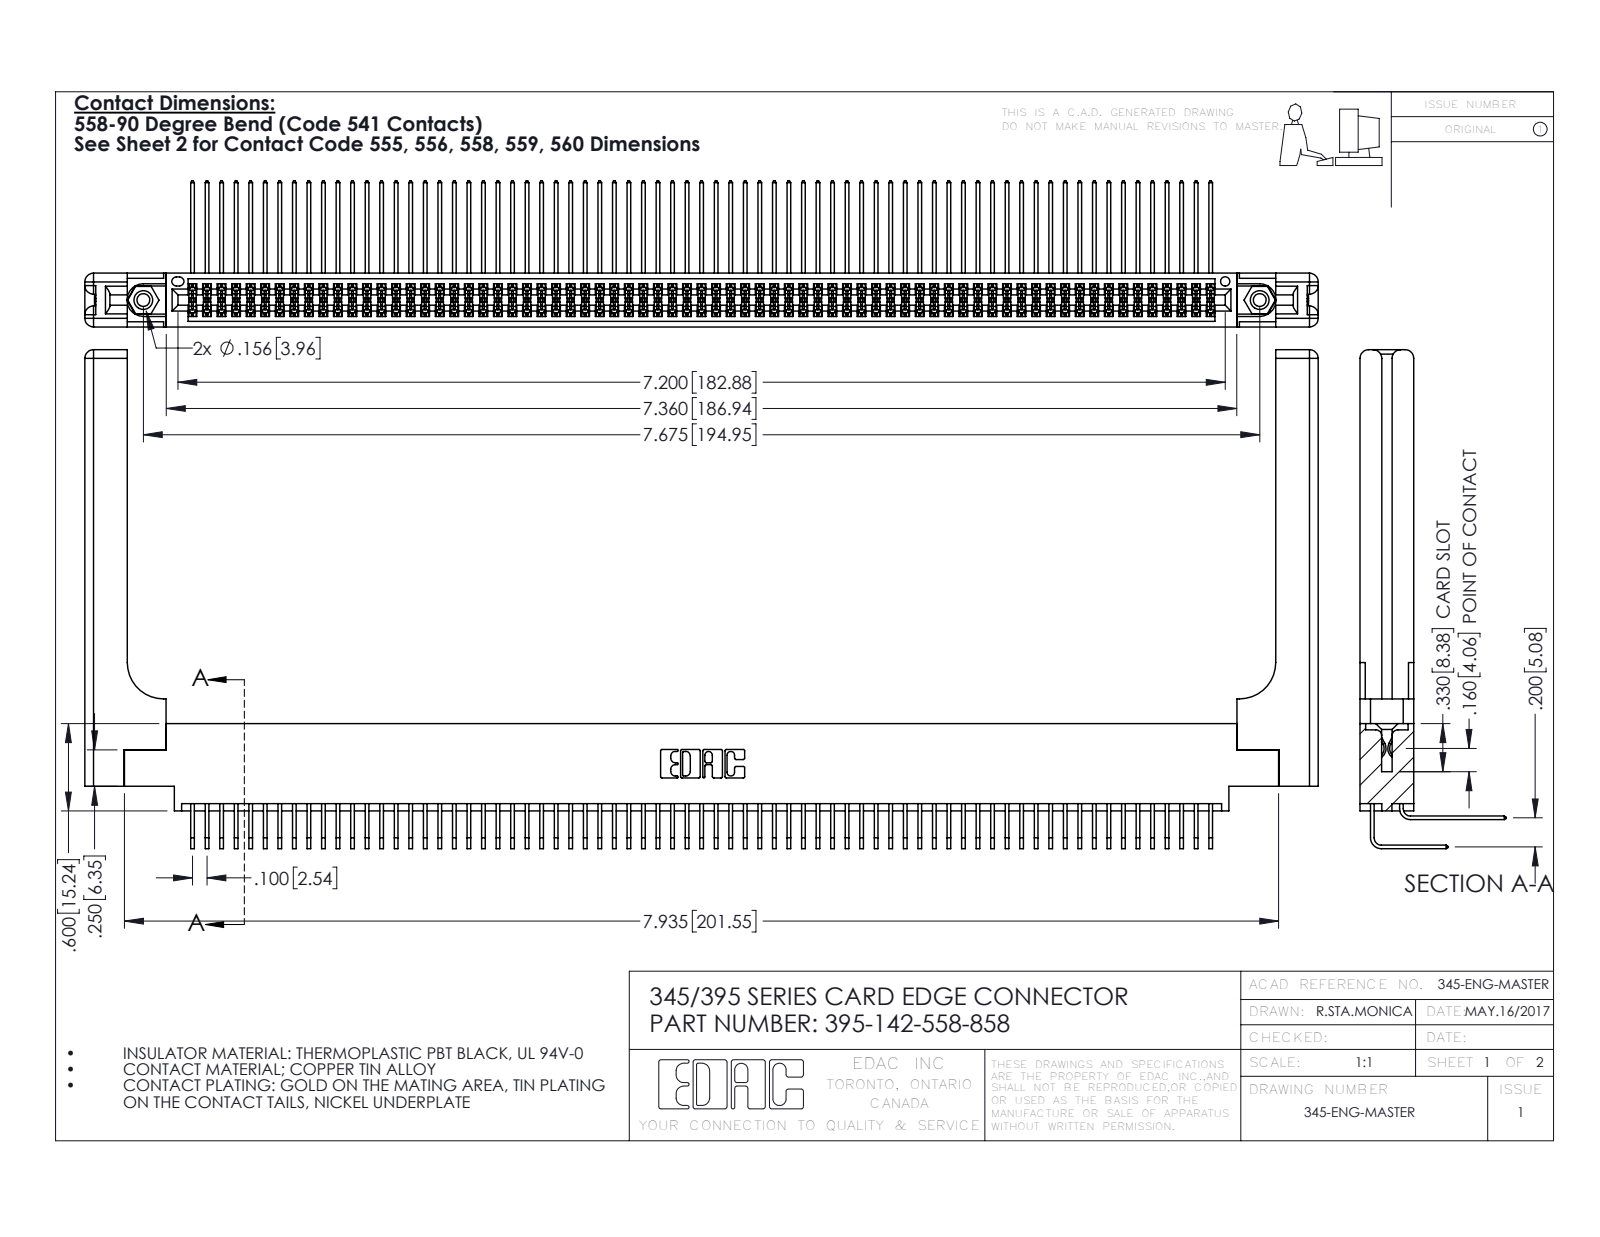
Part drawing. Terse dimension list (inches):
name: 345-250-001_345-250-001-102; 345 Part_0.170 Offset - 0.156 Dia-TH; 345-292-001_558 559 Tail - 1; 345-292-001_558 Tail - 2 (+2 more)
written by: SolidWorks 2016 (CONFIG_CONTROL_DESIGN)
unit: in
bodies: 147 solids, 7770 faces (5202 planar, 2508 cylindrical, 60 other)
size: 8.479 × 3.429 × 1.005
volume: 1.853 in³; area: 65.07 in²
holes: 2× ⌀0.089, 2× ⌀0.125, 2× ⌀0.156, 1× ⌀0.064
bosses: 2× ⌀0.155
rounds: 283× R0.006, 22× R0.01, 16× R0.06, 6× R0.007, 6× R0.031, 3× R0.026, 2× R0.014, 2× R0.019
face distances: 0.072, 0.298, 0.37, 0.2, 0.098, 0.272, 0.025, 0.225, 0.175, 0.025
hole spacings: 0.27, 7.439, 7.675
